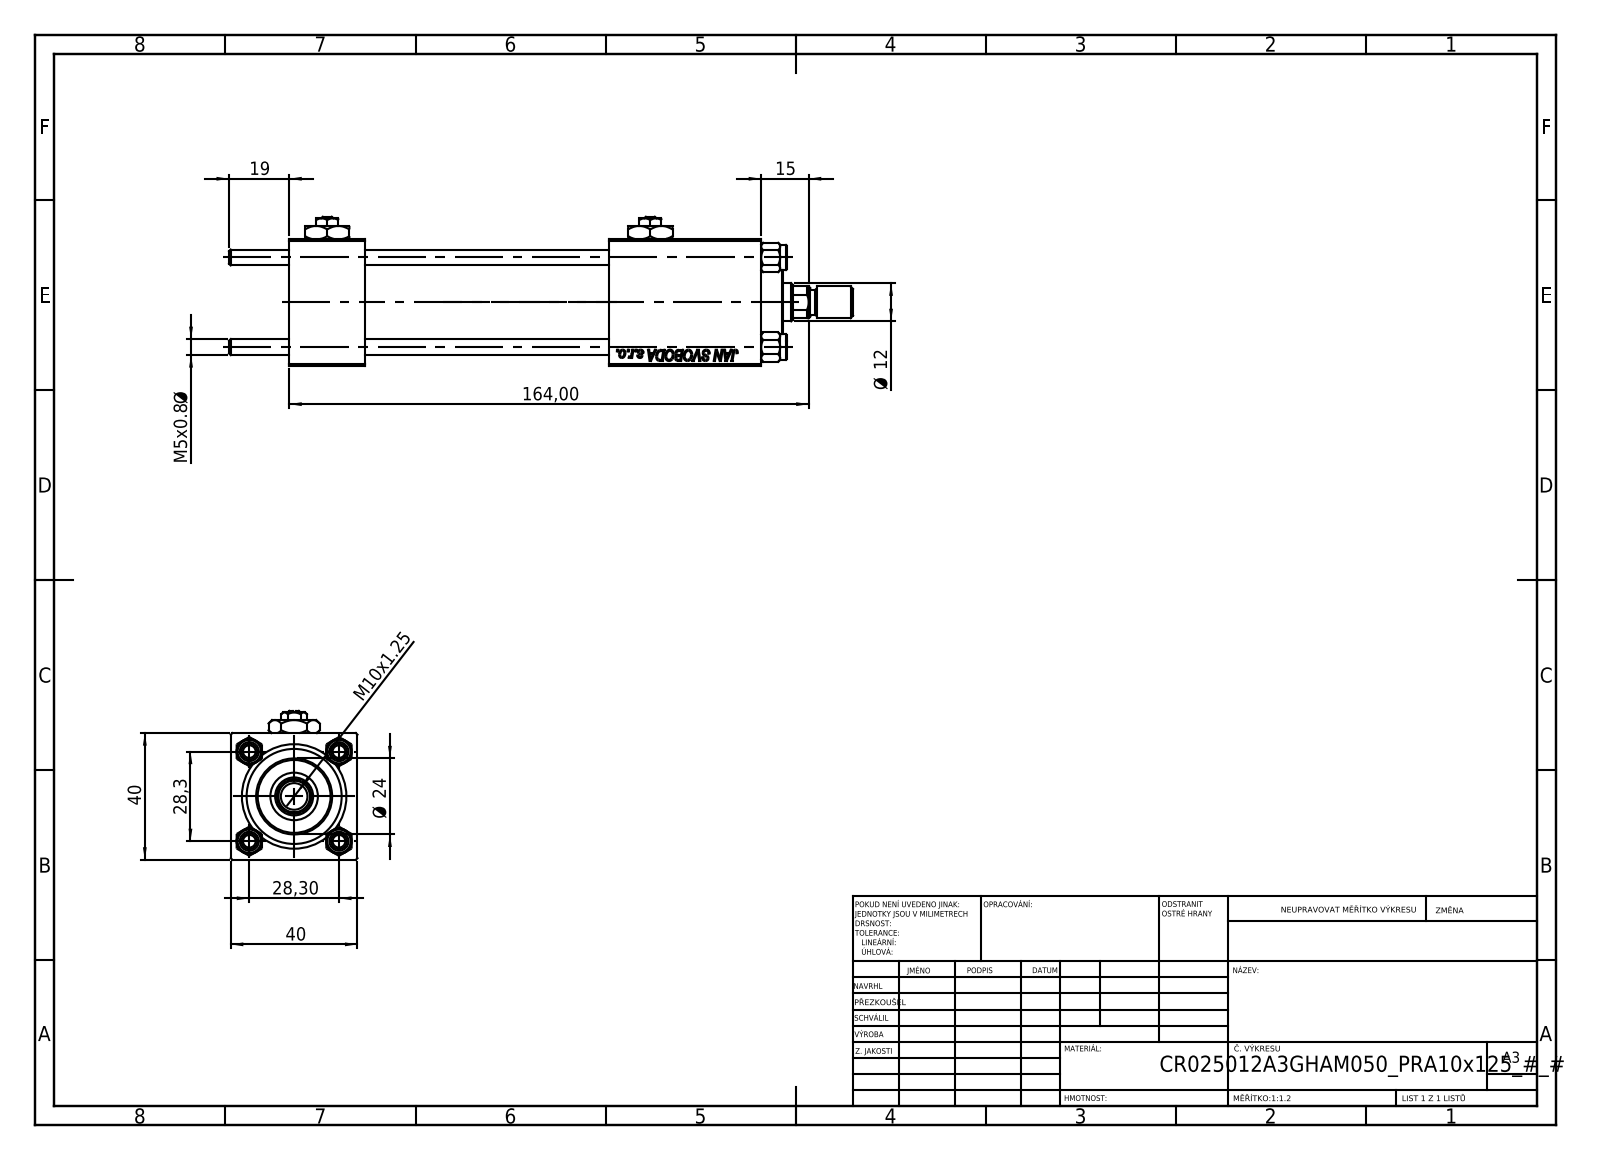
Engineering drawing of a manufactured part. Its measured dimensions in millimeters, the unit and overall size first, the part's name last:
Units: millimetres
Overall size (bounding box): 197 × 47 × 40
Round holes (diameter × count): ⌀5 ×4, ⌀20 ×3, ⌀7 ×2, ⌀13.16 ×2, ⌀6.5 ×1, ⌀12 ×1, ⌀15 ×1, ⌀25 ×1, ⌀30 ×1
Round bosses / shafts (diameter × count): ⌀8 ×5, ⌀31 ×1, ⌀24 ×1, ⌀10 ×1
Partial cylindrical surfaces — rounded edges, fillets, slot ends (radius × count): R5.5 ×1
Main face-to-face distances: 40, 24, 39.8, 149, 125, 77, 120.3, 96.3, 28.7, 101
Hole centre spacings: 20.01, 28.3, 40.02, 102
Volume: 158 117 mm³ · Surface area: 69 543 mm²
Bodies: 14 solids, 1246 faces (568 planar, 94 cylindrical, 584 other)
Part name (STEP PRODUCT): CR025_012_A_0_G_A_G_M_020_+#_##_TYCINKA; V215CR_BODY_A; V215_VC_A; NUT_M5 (+3 more)
STEP written by: SolidWorks 2019 (CONFIG_CONTROL_DESIGN)
